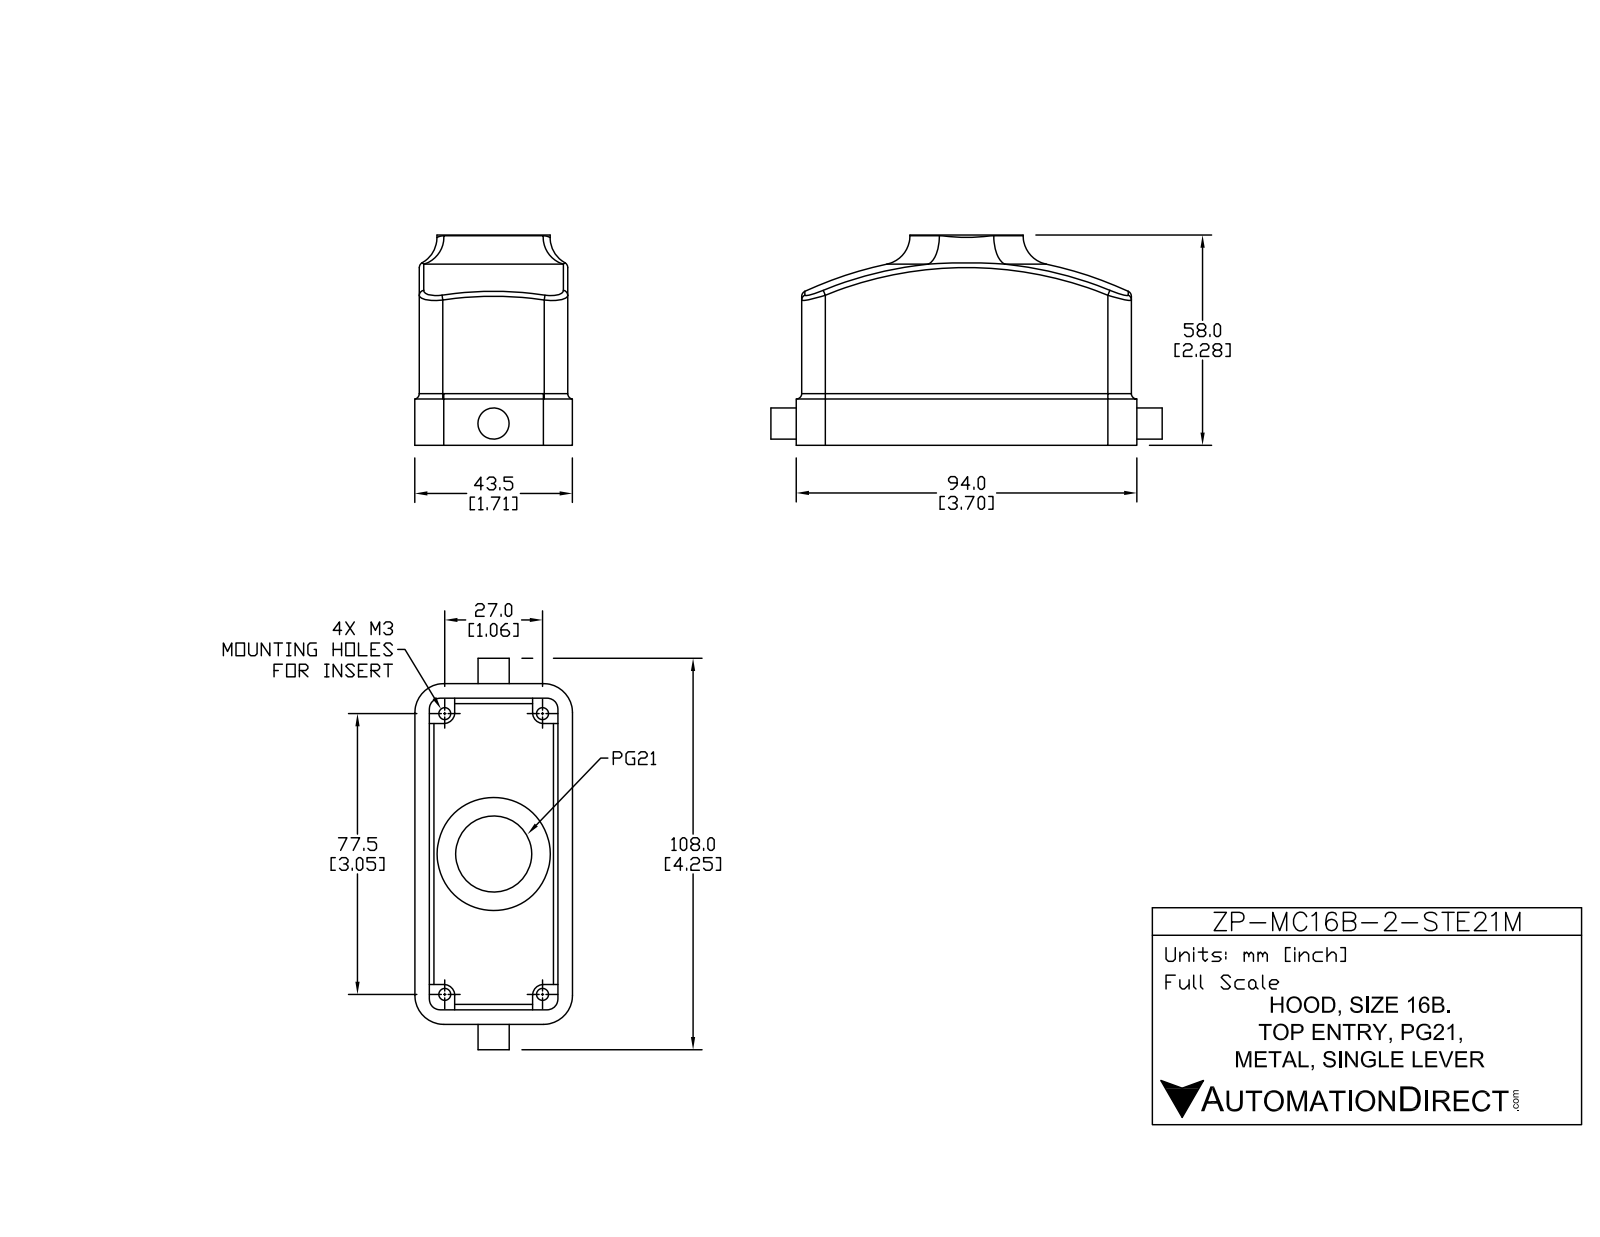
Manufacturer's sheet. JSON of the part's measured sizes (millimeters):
{"part_name": "ZP-MC16B-2-STE21M", "step_written_by": "SolidWorks 2011 (AUTOMOTIVE_DESIGN)", "units": "millimeters", "bodies": {"solids": 2, "faces": 96, "planar": 39, "cylindrical": 34, "other": 23}, "overall_size": [108, 58, 43.5], "volume_mm3": 62146, "surface_area_mm2": 31611, "round_holes": [[3.3, 4], [21, 1], [26, 1]], "round_bosses_or_shafts": [[31.25, 1], [8.6, 1]], "partial_cylinders_radius": [[3, 8], [1.5, 4], [5.5, 4], [6.5, 4], [8, 4]], "face_to_face_distances": [4, 37, 1.25, 38.25, 41, 33, 5.25, 42.25, 39.5, 2.75], "hole_center_spacings": [40.95, 26.5, 77.5, 81.91]}
